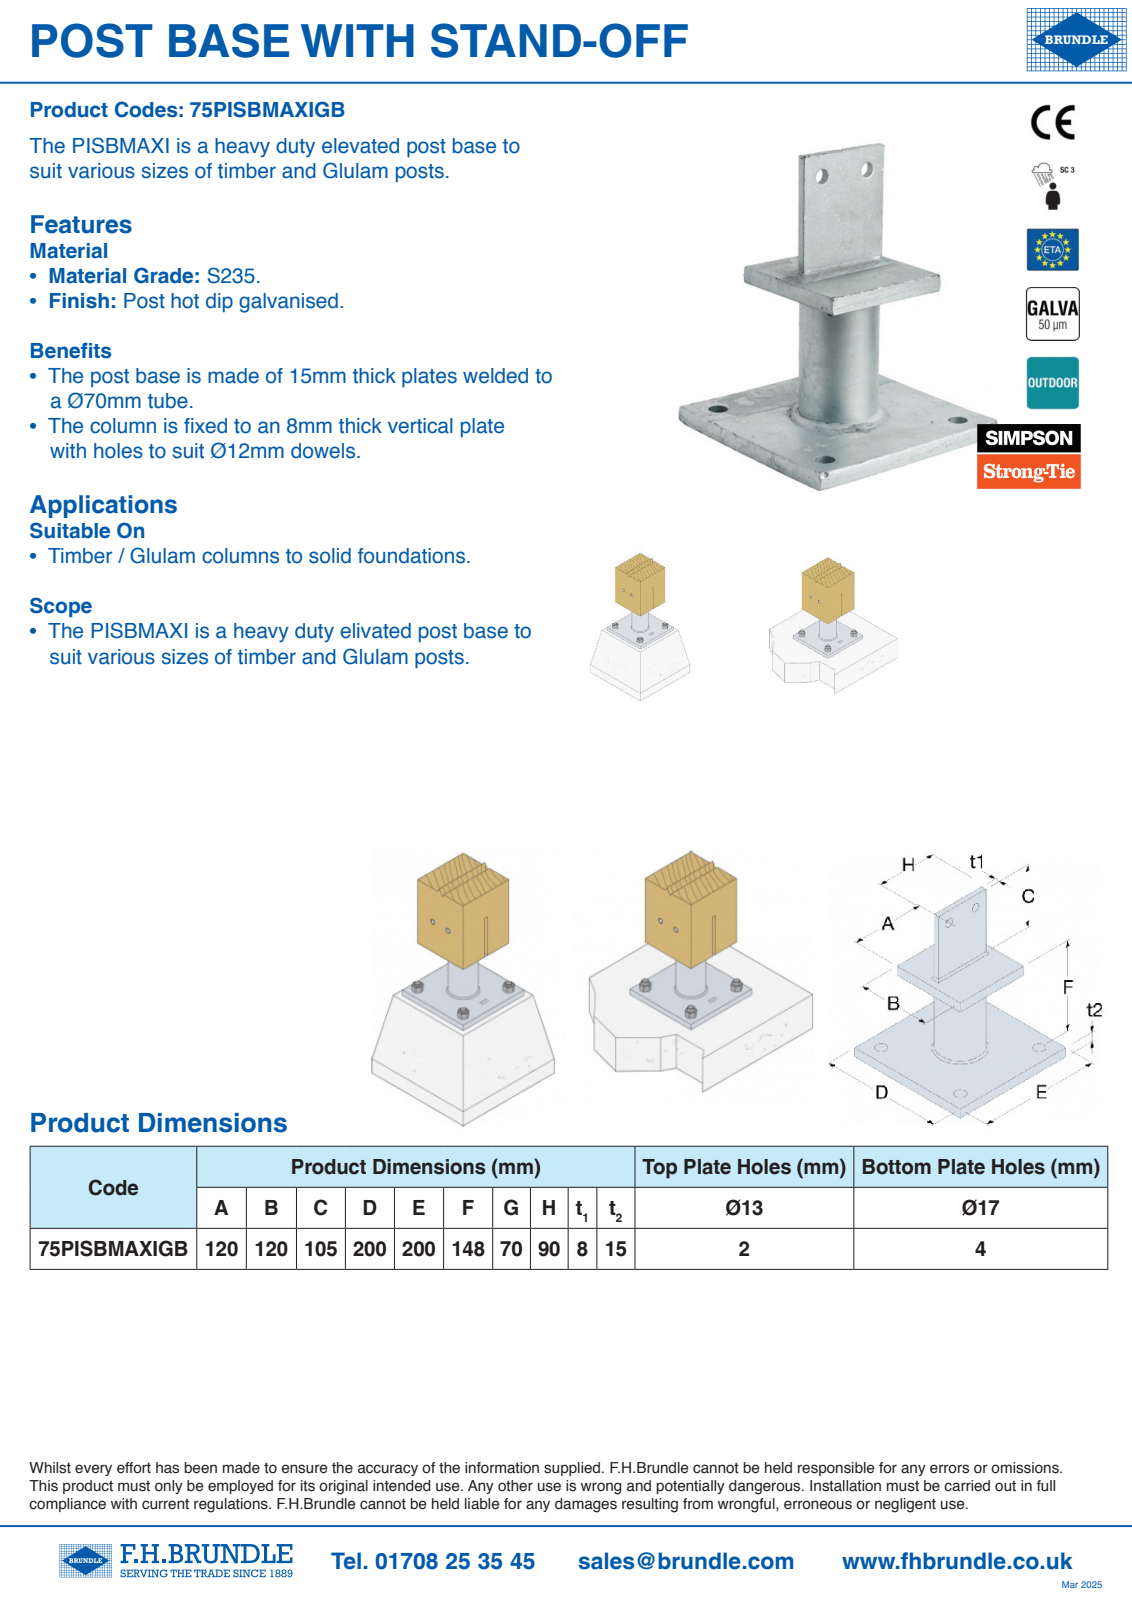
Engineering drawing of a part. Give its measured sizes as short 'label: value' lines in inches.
name: 75PISBMAXIGB
written by: SolidWorks 2023 (CONFIG_CONTROL_DESIGN)
unit: in
bodies: 1 solid, 41 faces (19 planar, 22 cylindrical, 0 other)
size: 9.961 × 7.874 × 7.874
volume: 60.44 in³; area: 304.8 in²
holes: 5× ⌀0.709, 2× ⌀0.512, 1× ⌀0.276, 1× ⌀2.362
bosses: 1× ⌀2.756
face distances: 0.591, 5.236, 5.827, 4.646, 0.315, 1.575, 6.299, 7.874, 3.78, 4.094
hole spacings: 4.176, 5.906, 4.633, 8.352, 1.969
